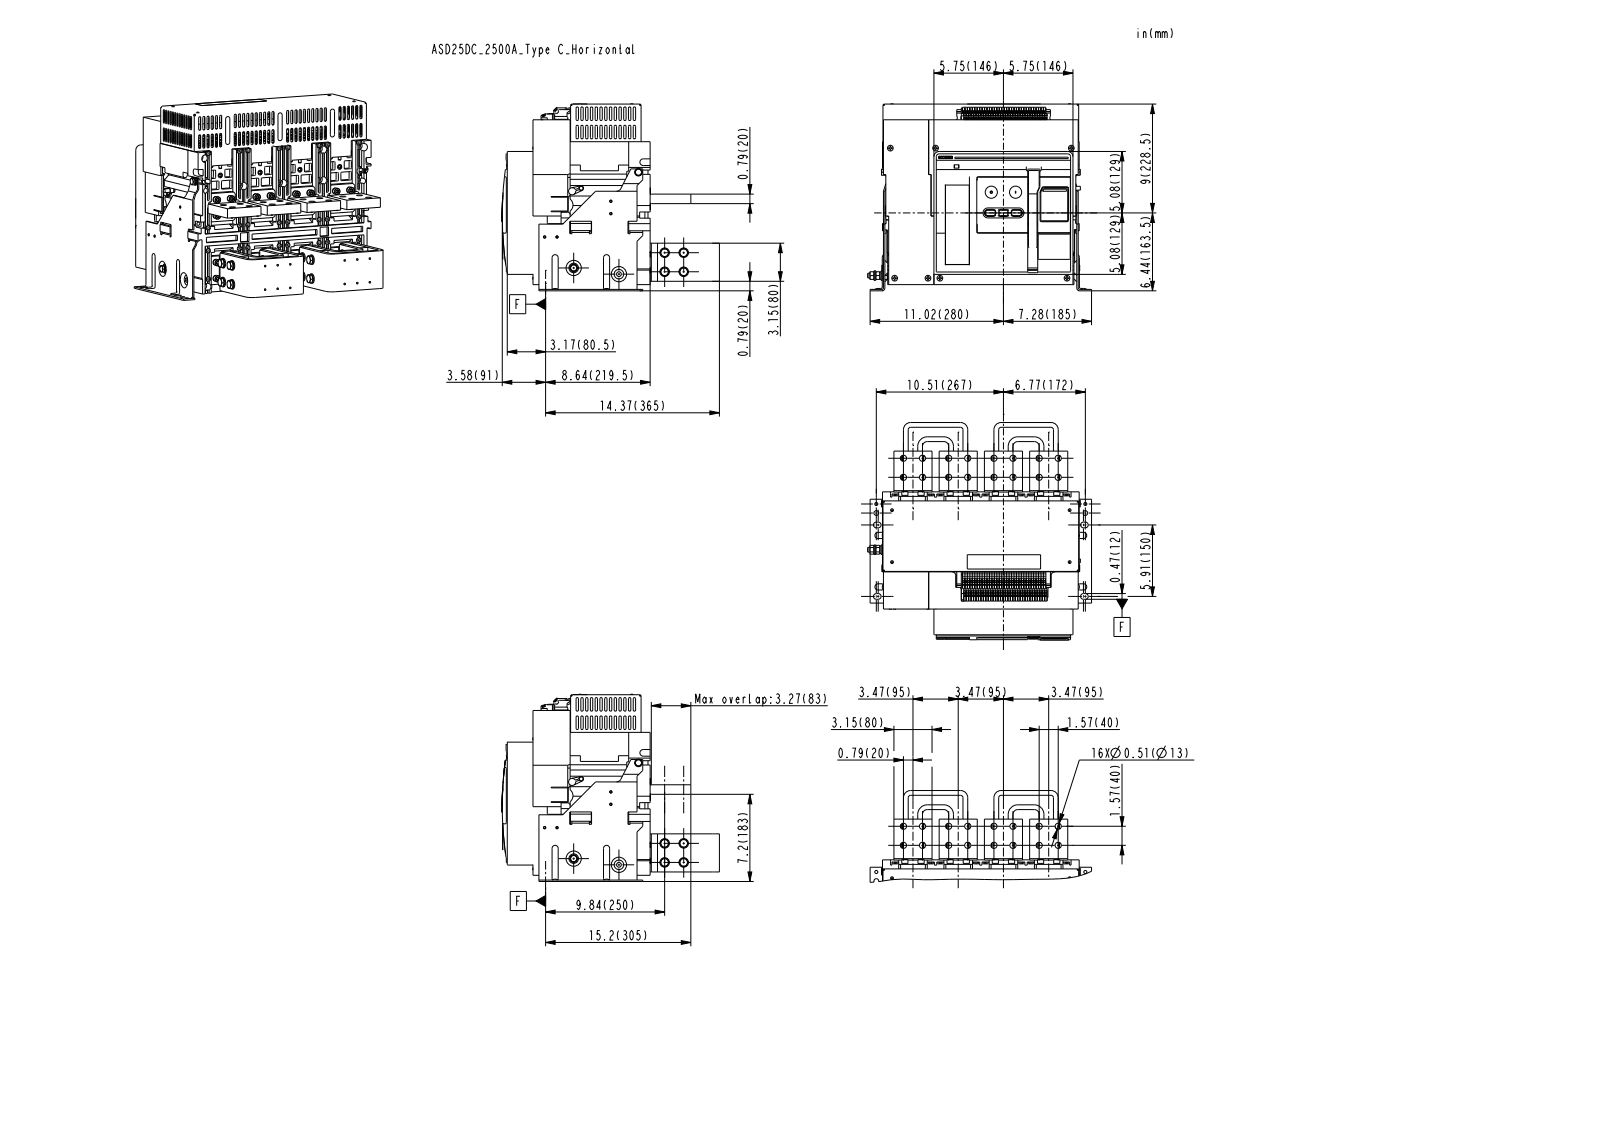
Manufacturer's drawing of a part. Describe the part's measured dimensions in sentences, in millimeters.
The part is named "PRT0002". Its 3-D file was written by "CREO PARAMETRIC BY PTC INC, 2020044 (CONFIG_CONTROL_DESIGN)". It is 17 solids with 14628 faces: 8889 planar, 4067 cylindrical and 1672 other. Overall it measures 470 by 456.91 by 392.92 millimeters. Its volume is 10 420 000 cubic millimeters and its surface area 3 543 000 square millimeters. Round holes: 104 of diameter 4, 43 of diameter 8.5, 39 of diameter 8.1, 29 of diameter 10, 25 of diameter 6.5, 24 of diameter 3, 23 of diameter 4.92, 20 of diameter 13, 16 of diameter 12, 11 of diameter 15.5, 10 of diameter 6.2, 9 of diameter 9. Round bosses or shafts: 47 of diameter 8, 34 of diameter 12.3, 34 of diameter 6.65, 32 of diameter 13, 26 of diameter 6, 24 of diameter 4, 22 of diameter 9, 12 of diameter 10. Partial cylindrical surfaces (rounded edges, fillets, slot ends): 269 of radius 2, 187 of radius 2.5, 157 of radius 1, 66 of radius 3, 41 of radius 0.5, 35 of radius 1.5, 32 of radius 5.25, 24 of radius 0.2. The main face-to-face distances are 4, 95, 1.5, 190, 377.5, 3, 8, 1, 156, 147.5. The hole center spacings are 40, 95, 103.08, 56.57, 190, 194.16, 55, 68.01.
